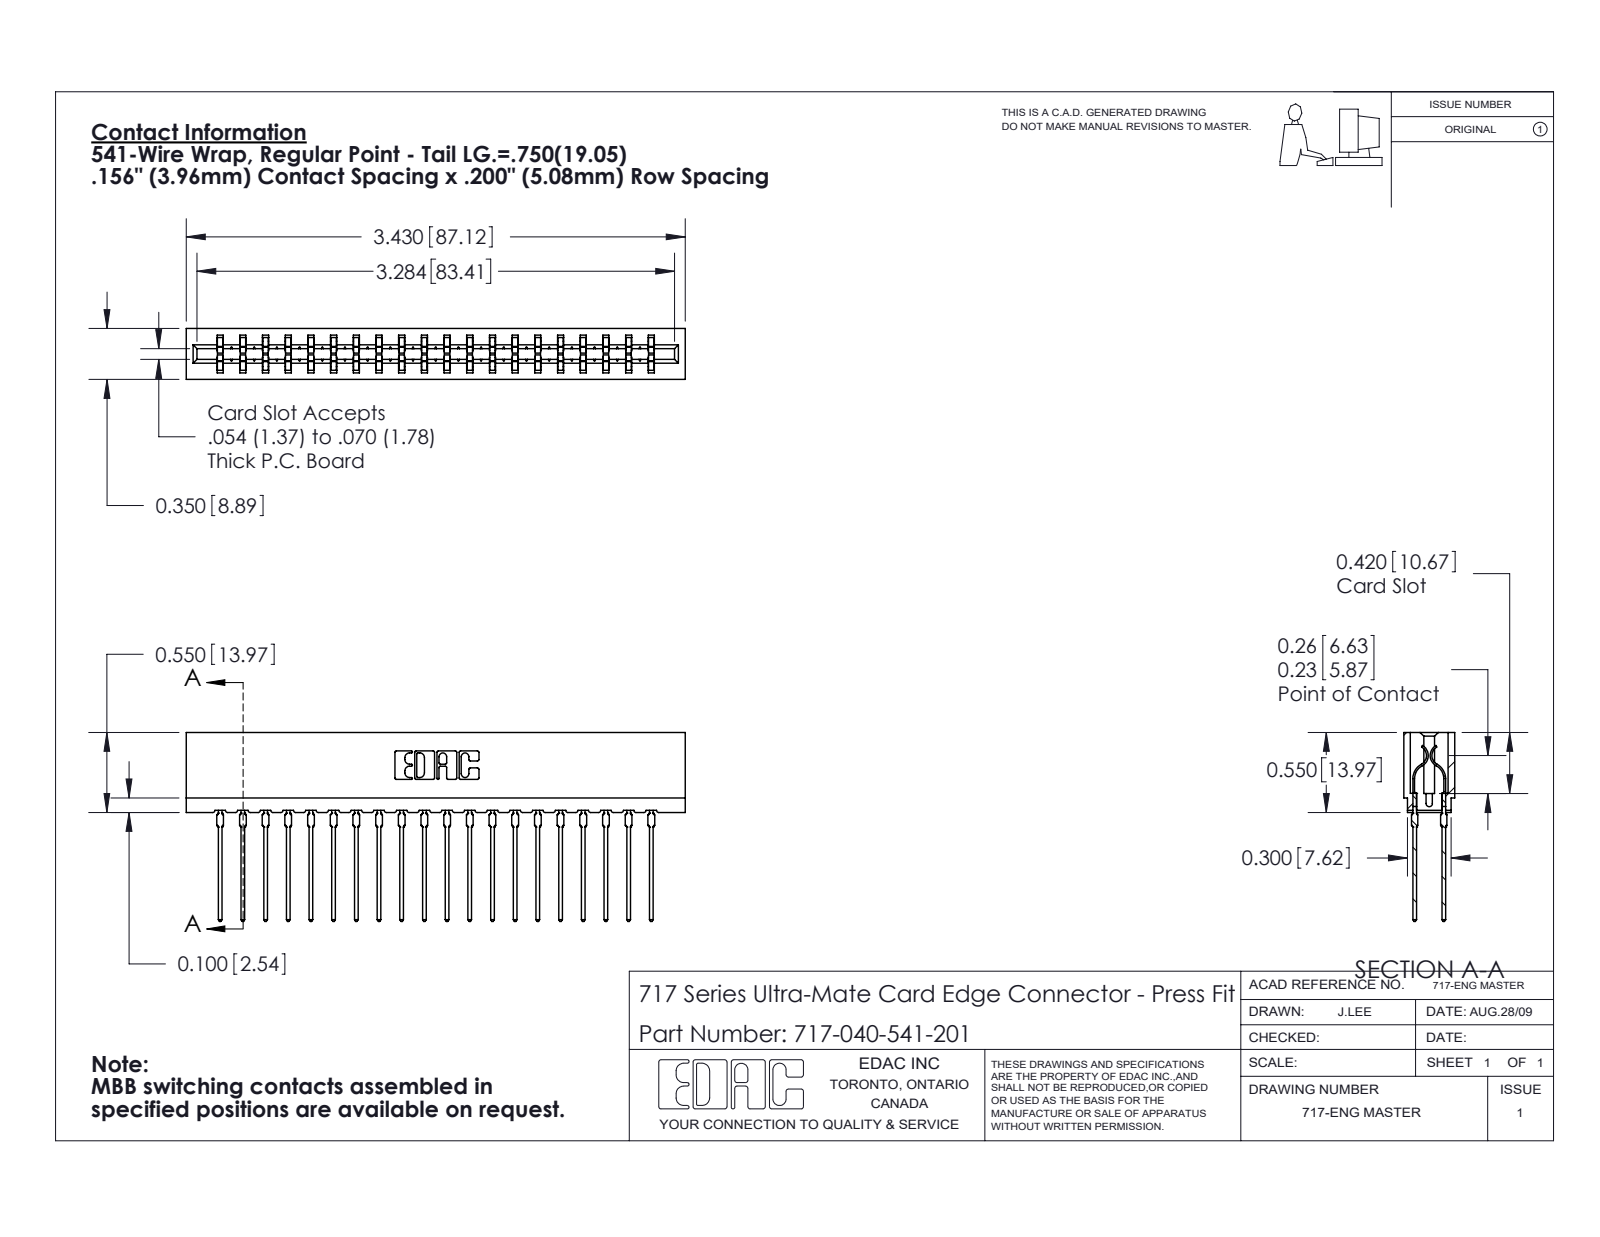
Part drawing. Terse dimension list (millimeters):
name: 717 Part_Insulator Option - 06; 745-292-001_541; 717-040-541-201
written by: SolidWorks 2020 (CONFIG_CONTROL_DESIGN)
unit: mm
bodies: 41 solids, 3694 faces (1914 planar, 740 cylindrical, 1040 other)
size: 87.1 × 33 × 8.9
volume: 7 830 mm³; area: 12 580 mm²
rounds: 80× R0.5, 40× R0.4, 22× R0.3, 8× R0.1, 8× R0.3, 6× R0.2, 6× R0.8, 3× R0.7
face distances: 5.4, 3.5, 8.9, 1.6, 7.3, 1.9, 3.8, 4, 2.2, 6.7
